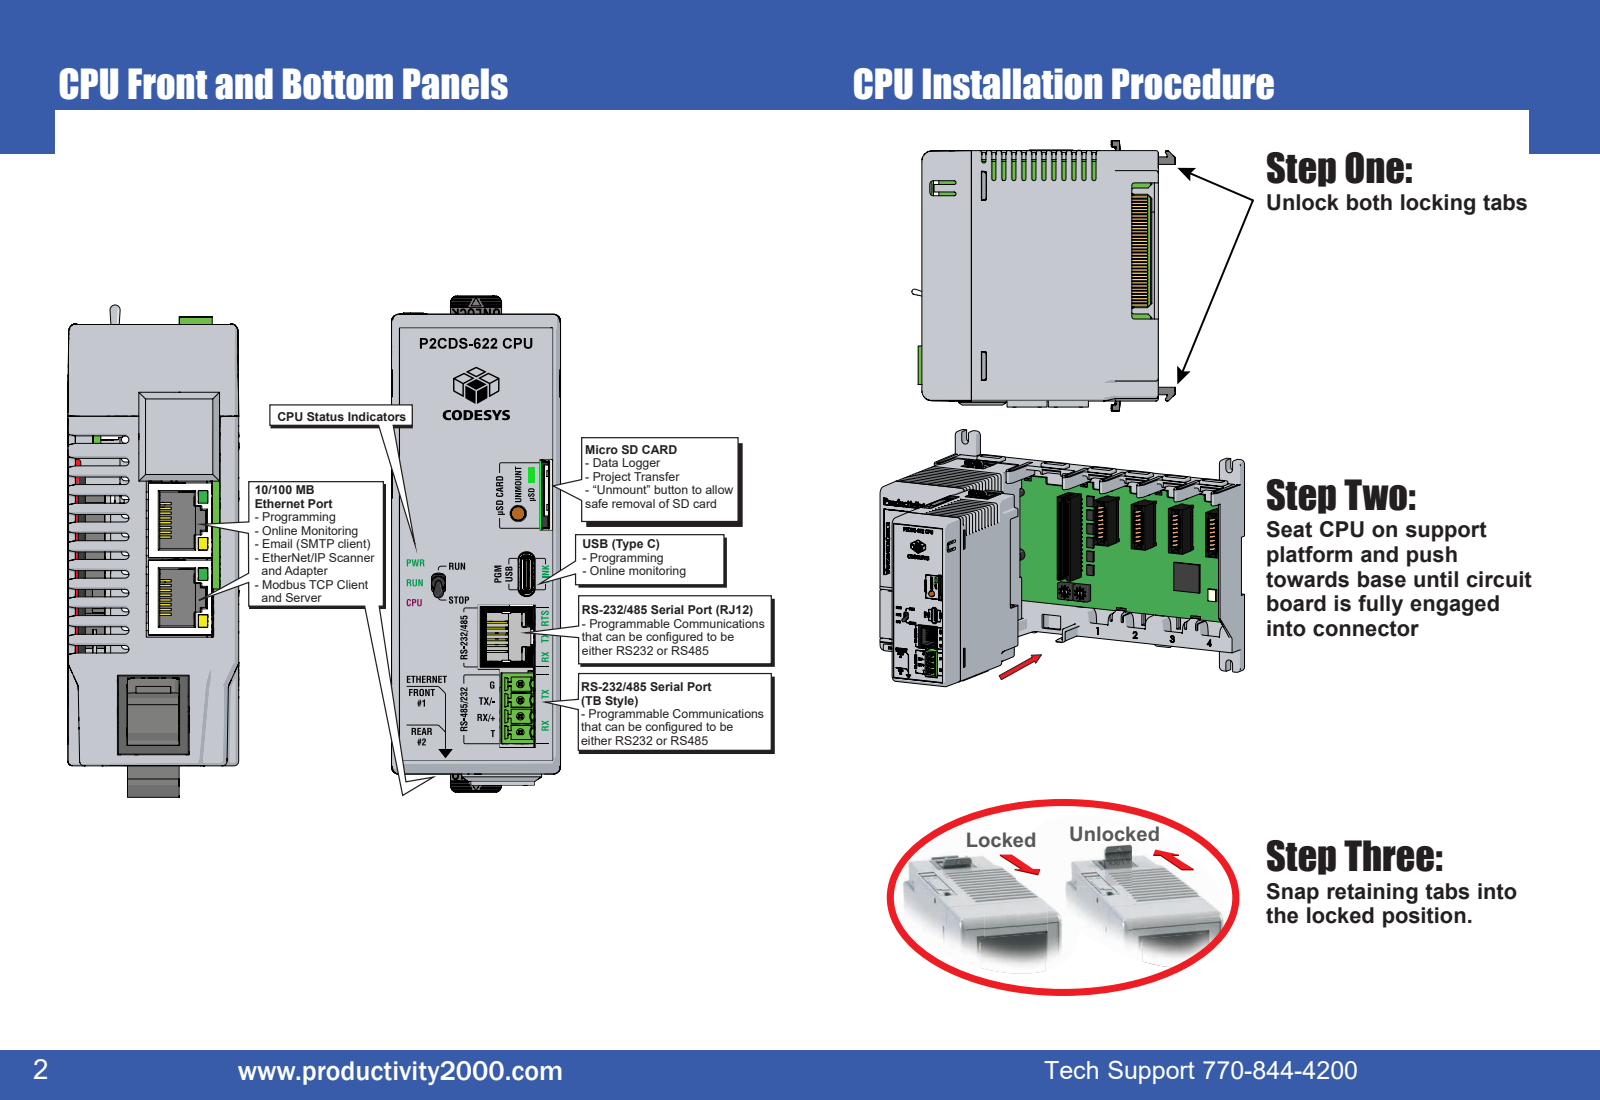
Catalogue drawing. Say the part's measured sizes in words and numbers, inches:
The part is named "P2CDS-622". Its 3-D file was written by "SolidWorks 2021 (AUTOMOTIVE_DESIGN)". It is 23 solids with 3979 faces: 2836 planar, 497 cylindrical and 646 other. Overall it measures 4.257 by 4.141 by 1.443 inches. Its volume is 2.241 cubic inches and its surface area 128.7 square inches. Round holes: 1 of diameter 0.049, 1 of diameter 0.079, 1 of diameter 0.123, 1 of diameter 0.126, 1 of diameter 0.148, 1 of diameter 0.185. Round bosses or shafts: 3 of diameter 0.063, 1 of diameter 0.186, 1 of diameter 0.118. Partial cylindrical surfaces (rounded edges, fillets, slot ends): 163 of radius 0.02, 72 of radius 0.039, 15 of radius 0.063, 14 of radius 0.016, 14 of radius 0.028, 14 of radius 0.059, 12 of radius 0.008, 5 of radius 0.031. The main face-to-face distances are 1.433, 1.423, 1.423, 1.413, 0.063, 1.37, 2.824, 0.015, 2.824, 0.87. The hole center spacings are 0.413, 1.462, 1.463, 1.876, 1.876.
